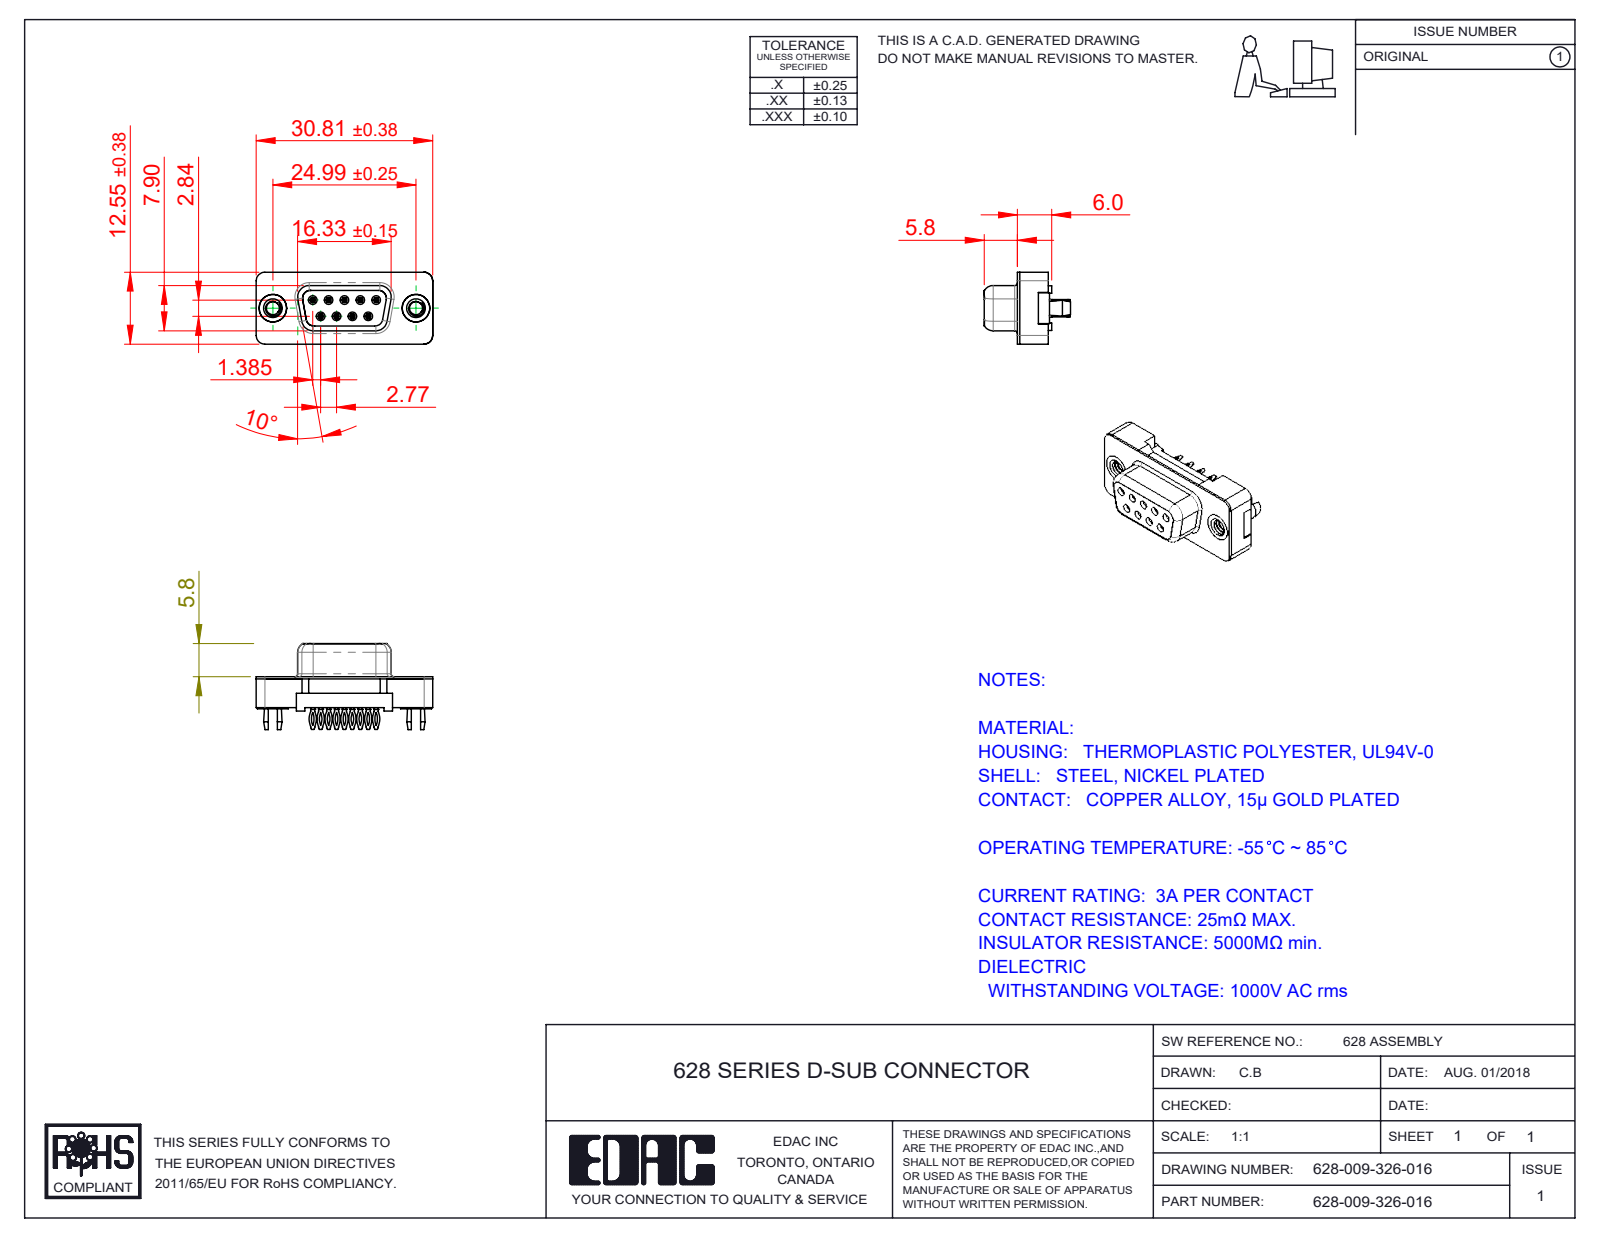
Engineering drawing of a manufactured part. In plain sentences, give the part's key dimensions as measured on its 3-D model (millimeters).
The part is named "628 Plastic Body Housing_09 Contacts; 628 PB Shell_09 Contacts; 628-009-326-016; 628 PB Contact Row 1_26 (+2 more)". Its 3-D file was written by "SolidWorks 2020 (CONFIG_CONTROL_DESIGN)". It is 13 solids with 1071 faces: 442 planar, 278 cylindrical and 351 other. Overall it measures 30.82 by 15.05 by 12.55 millimeters. Its volume is 1 988 cubic millimeters and its surface area 4 430 square millimeters. Round holes: 9 of diameter 0.9, 2 of diameter 2.26, 2 of diameter 3.05, 2 of diameter 4, 2 of diameter 4.8, 2 of diameter 5. Round bosses or shafts: 2 of diameter 4.9. Partial cylindrical surfaces (rounded edges, fillets, slot ends): 36 of radius 0.25, 18 of radius 2.92, 18 of radius 3.33, 13 of radius 0.5, 11 of radius 1.35, 9 of radius 0.3, 8 of radius 1.5, 4 of radius 0.9. The main face-to-face distances are 0.4, 2, 5.54, 2.77, 2.5, 5, 5.4, 6.2, 2.7, 8.7. The hole center spacings are 3.16, 2.77, 5.54, 5.03, 5.04, 8.31, 7.1, 7.48.
